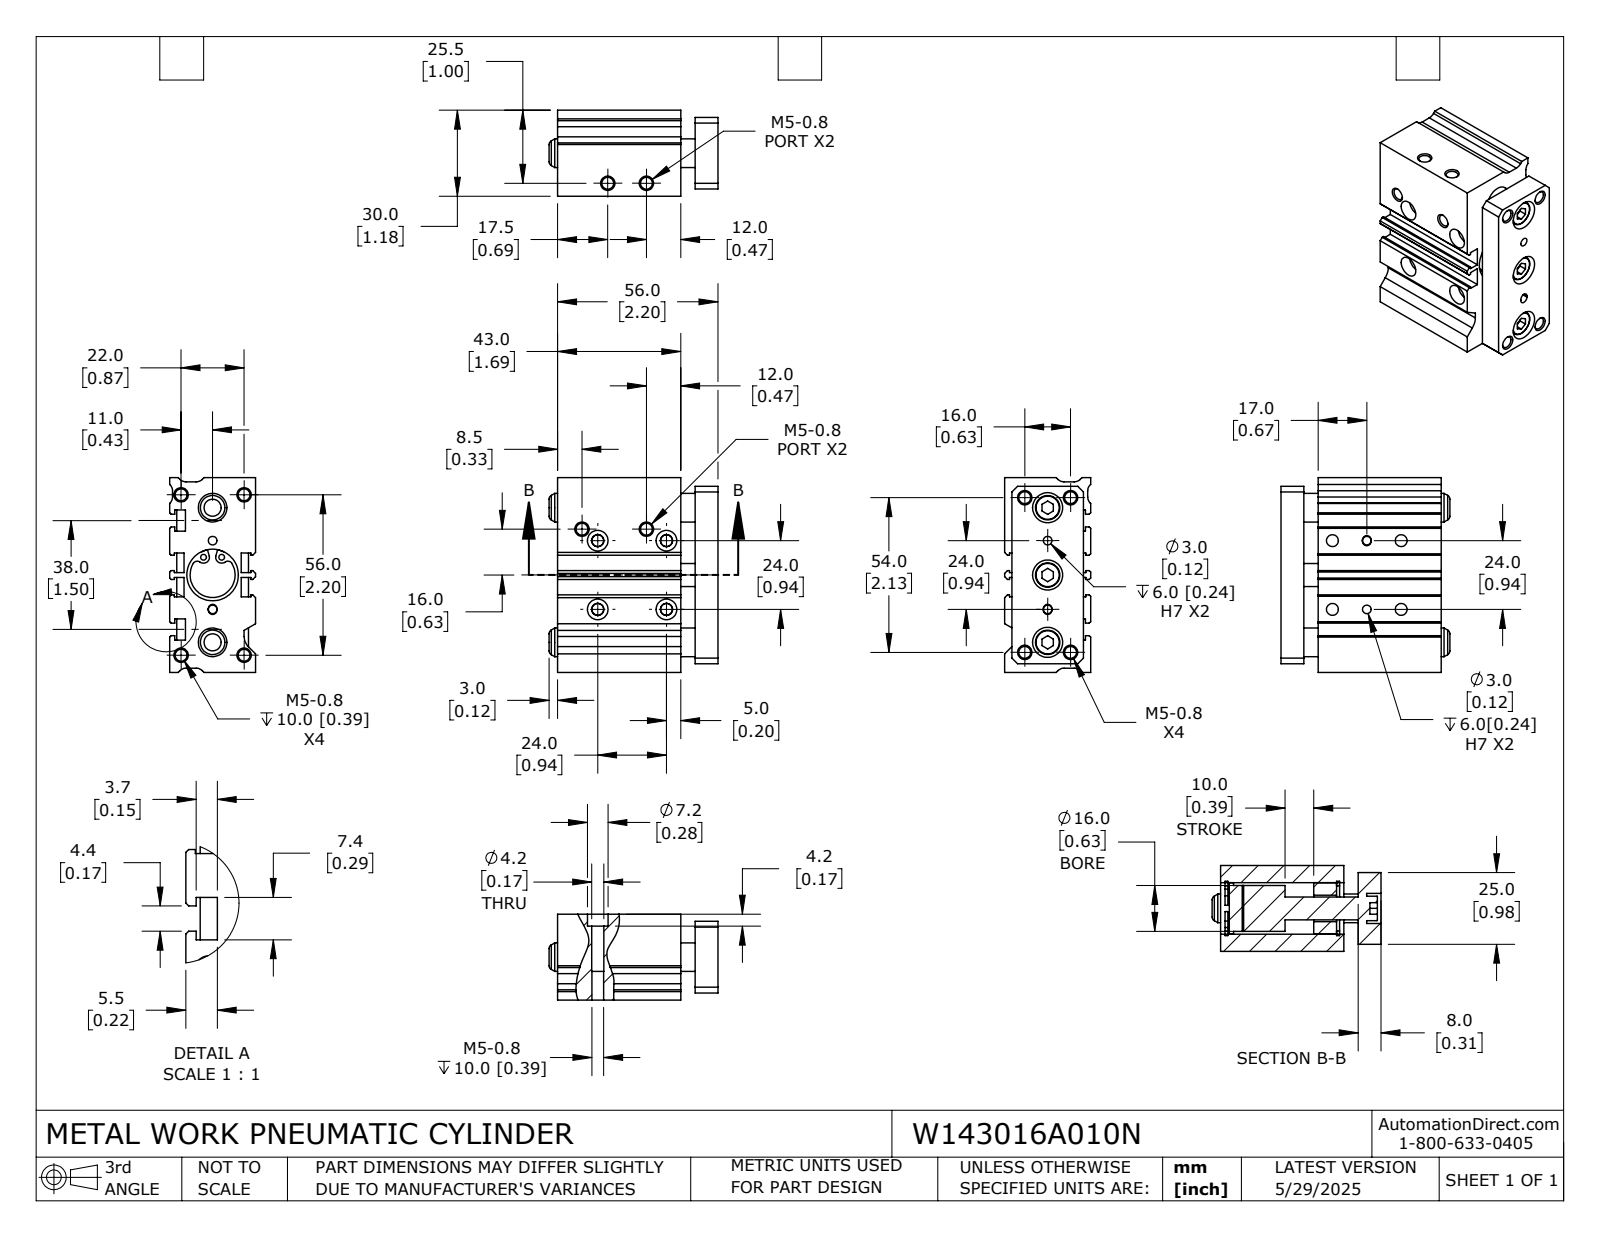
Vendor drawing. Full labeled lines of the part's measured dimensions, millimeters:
Part name (STEP PRODUCT): W143016A010_ROD; W143016A010_BODY; W143016A010N
STEP written by: SolidWorks 2024 (CONFIG_CONTROL_DESIGN)
Units: millimetres
Bodies: 6 solids, 344 faces (169 planar, 137 cylindrical, 38 other)
Overall size (bounding box): 68 × 59 × 30
Volume: 81 920 mm³ · Surface area: 35 809 mm²
Round holes (diameter × count): ⌀4.13 ×16, ⌀2 ×4, ⌀3 ×4, ⌀4.2 ×4, ⌀7.2 ×4, ⌀10.5 ×3, ⌀10 ×2, ⌀9.2 ×1, ⌀15.7 ×1
Round bosses / shafts (diameter × count): ⌀8.5 ×3, ⌀19 ×2, ⌀18 ×1, ⌀16 ×1, ⌀8 ×1
Partial cylindrical surfaces — rounded edges, fillets, slot ends (radius × count): R3 ×6, R1.5 ×4, R1.58 ×4, R2.07 ×4, R5 ×1
Main face-to-face distances: 5, 2.5, 25, 8, 30, 48, 43, 3, 1.5, 13
Hole centre spacings: 12, 24, 3.16, 6.62, 6.95, 8.73, 11.88, 17
